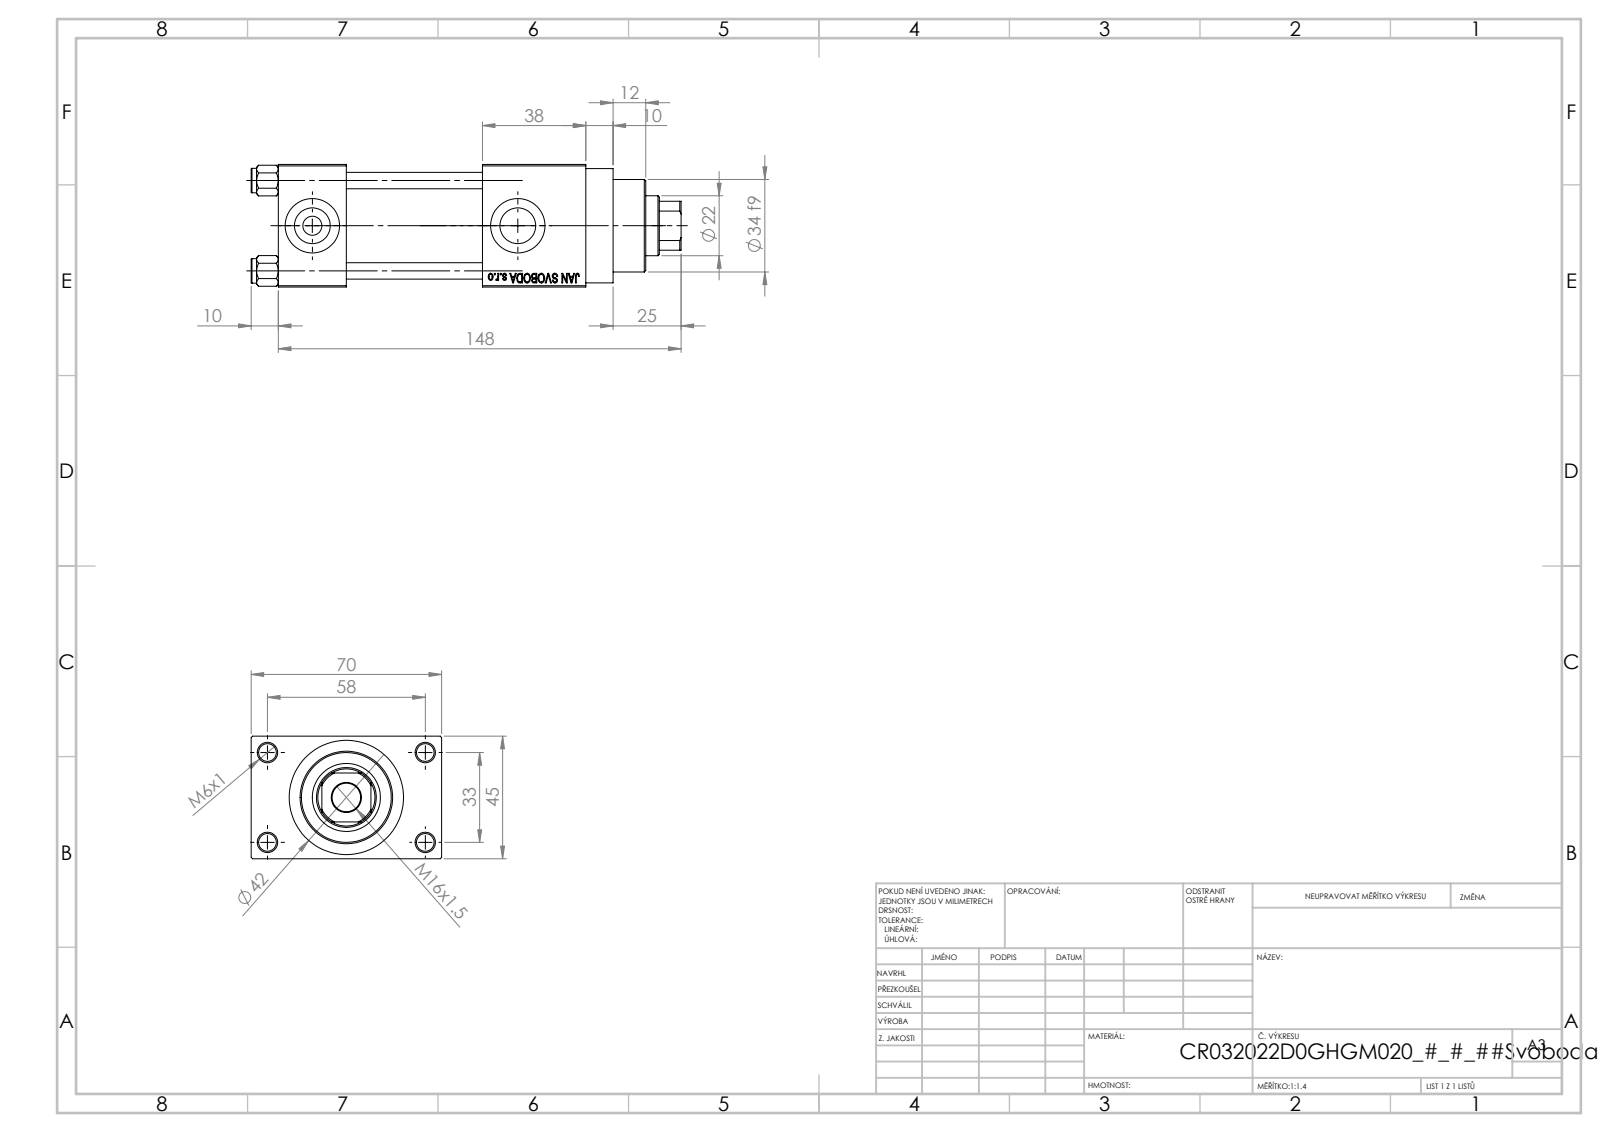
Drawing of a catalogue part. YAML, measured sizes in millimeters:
part_name: "NUT_M5_D; V215CR_D_Body; V215CR_VCP_D; V215_VC_A (+1 more)"
step_written_by: "SolidWorks 2019 (CONFIG_CONTROL_DESIGN)"
units: millimeters
bodies: {solids: 11, faces: 1102, planar: 496, cylindrical: 88, other: 518}
overall_size: [158, 70, 45]
volume: 242996
surface_area: 79972
round_holes:
  - {diameter: 6, count: 4}
  - {diameter: 6.5, count: 4}
  - {diameter: 7, count: 2}
  - {diameter: 13.16, count: 2}
  - {diameter: 20, count: 2}
  - {diameter: 10.5, count: 1}
  - {diameter: 22, count: 1}
  - {diameter: 24, count: 1}
  - {diameter: 25, count: 1}
  - {diameter: 32, count: 1}
  - {diameter: 33, count: 1}
round_bosses_or_shafts:
  - {diameter: 9, count: 4}
  - {diameter: 42, count: 1}
  - {diameter: 38, count: 1}
  - {diameter: 34, count: 1}
partial_cylinders:
  - {radius: 10.5, count: 1}
face_to_face_distances: [45, 25, 50, 12.5, 75, 57.5, 88, 38, 113, 70]
hole_center_spacings: [12.4, 23.48, 33.2, 33.37, 35.35, 45.6, 56.35, 33]
